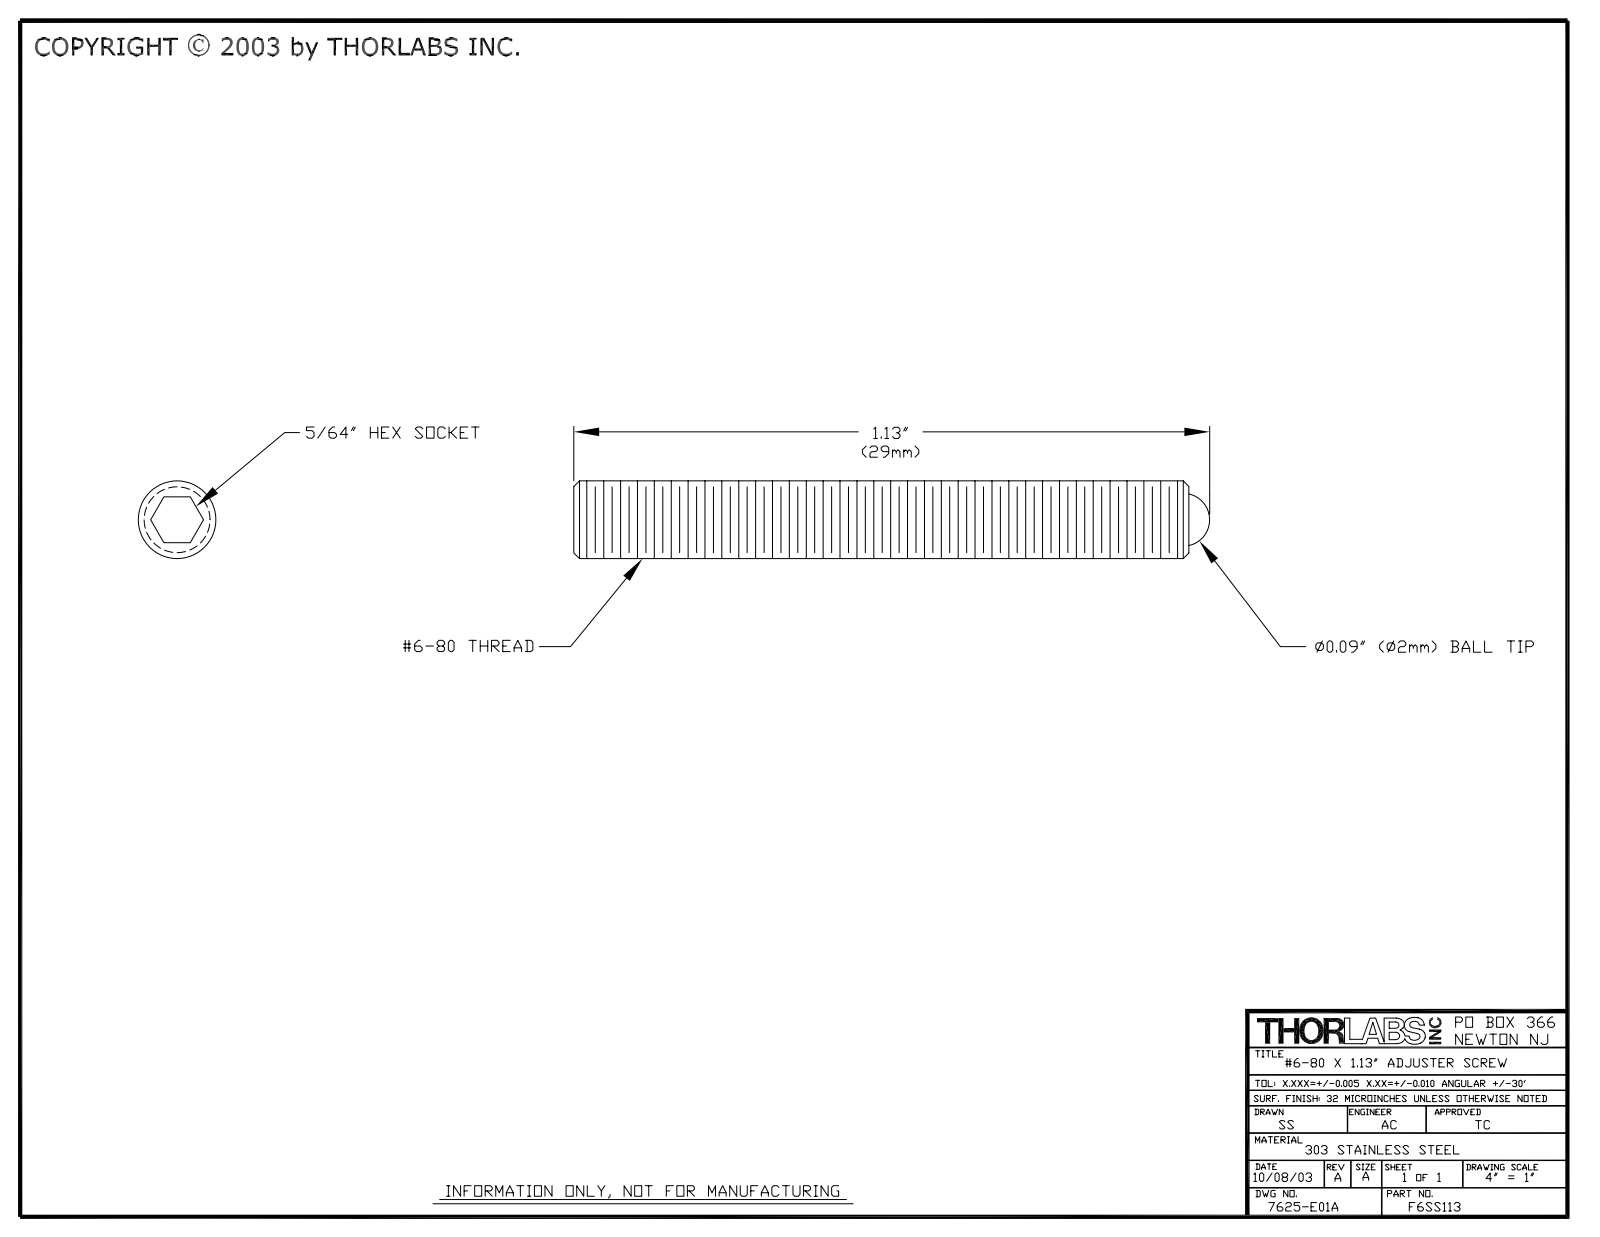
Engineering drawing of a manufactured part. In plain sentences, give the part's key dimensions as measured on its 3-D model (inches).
The part is named "7625-E0W". Its 3-D file was written by "SolidWorks 2011 (AUTOMOTIVE_DESIGN)". It is 2 solids with 199 faces: 10 planar, 177 cylindrical and 12 other. Overall it measures 1.13 by 0.138 by 0.138 inches. Its volume is 0.014 cubic inches and its surface area 0.91 square inches. Round holes: 1 of diameter 0.094. Round bosses or shafts: 1 of diameter 0.138, 1 of diameter 0.117. The main face-to-face distances are 0.066, 1.093, 0.973, 0.12.
